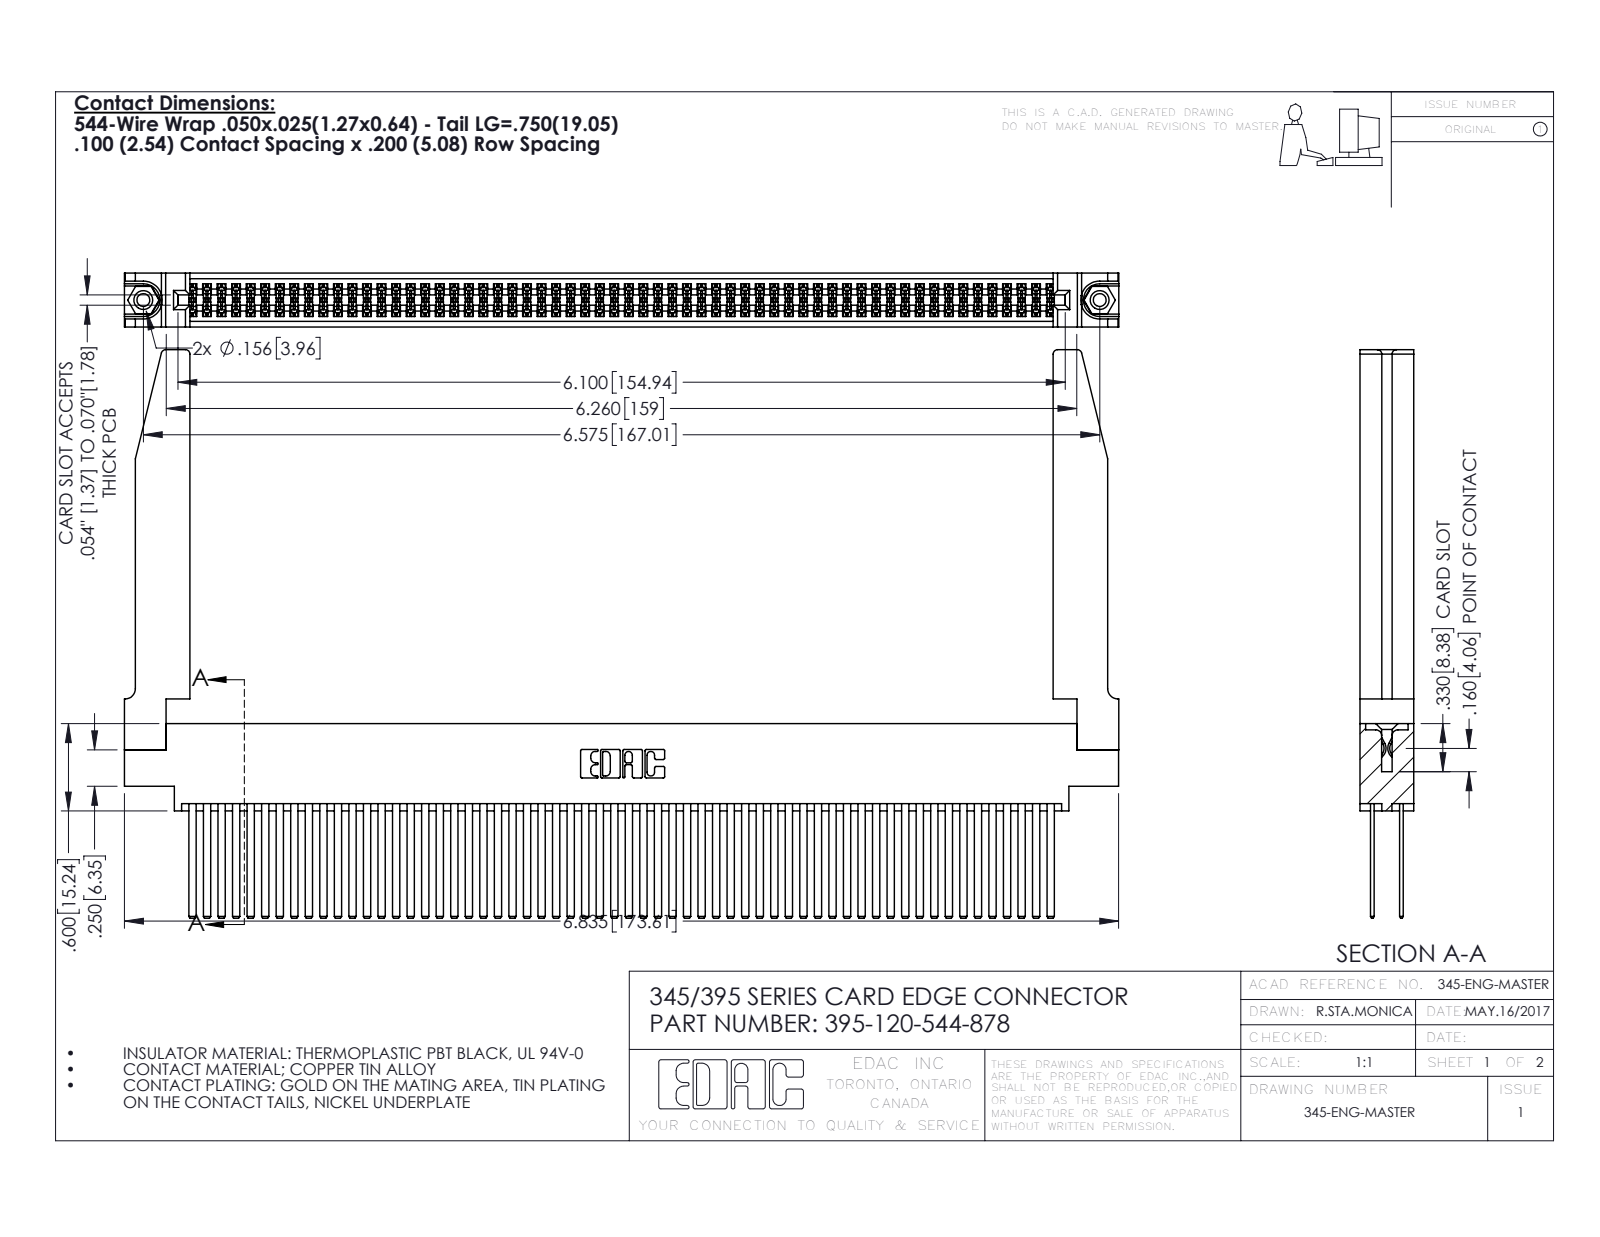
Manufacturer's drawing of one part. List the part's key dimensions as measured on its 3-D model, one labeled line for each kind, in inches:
Part name (STEP PRODUCT): 395-120-544-878; 345-250-001_345-250-001-102; 345 Part_0.170 Offset - 0.156 Dia-TH; 345-292-001_345-293-144 (+1 more)
STEP written by: SolidWorks 2016 (CONFIG_CONTROL_DESIGN)
Units: inches
Bodies: 125 solids, 5644 faces (3706 planar, 1886 cylindrical, 52 other)
Overall size (bounding box): 6.836 × 3.907 × 0.37
Volume: 1.609 in³ · Surface area: 61.63 in²
Round holes (diameter × count): ⌀0.089 ×2, ⌀0.125 ×2, ⌀0.156 ×2, ⌀0.064 ×1
Round bosses / shafts (diameter × count): ⌀0.155 ×2
Partial cylindrical surfaces — rounded edges, fillets, slot ends (radius × count): R0.006 ×180, R0.01 ×22, R0.03 ×8, R0.007 ×6, R0.031 ×6, R0.026 ×3, R0.014 ×2, R0.019 ×2
Main face-to-face distances: 0.072, 0.298, 0.098, 0.272, 0.025, 0.2, 0.37, 0.225, 0.175, 0.148
Hole centre spacings: 0.27, 6.339, 6.575
